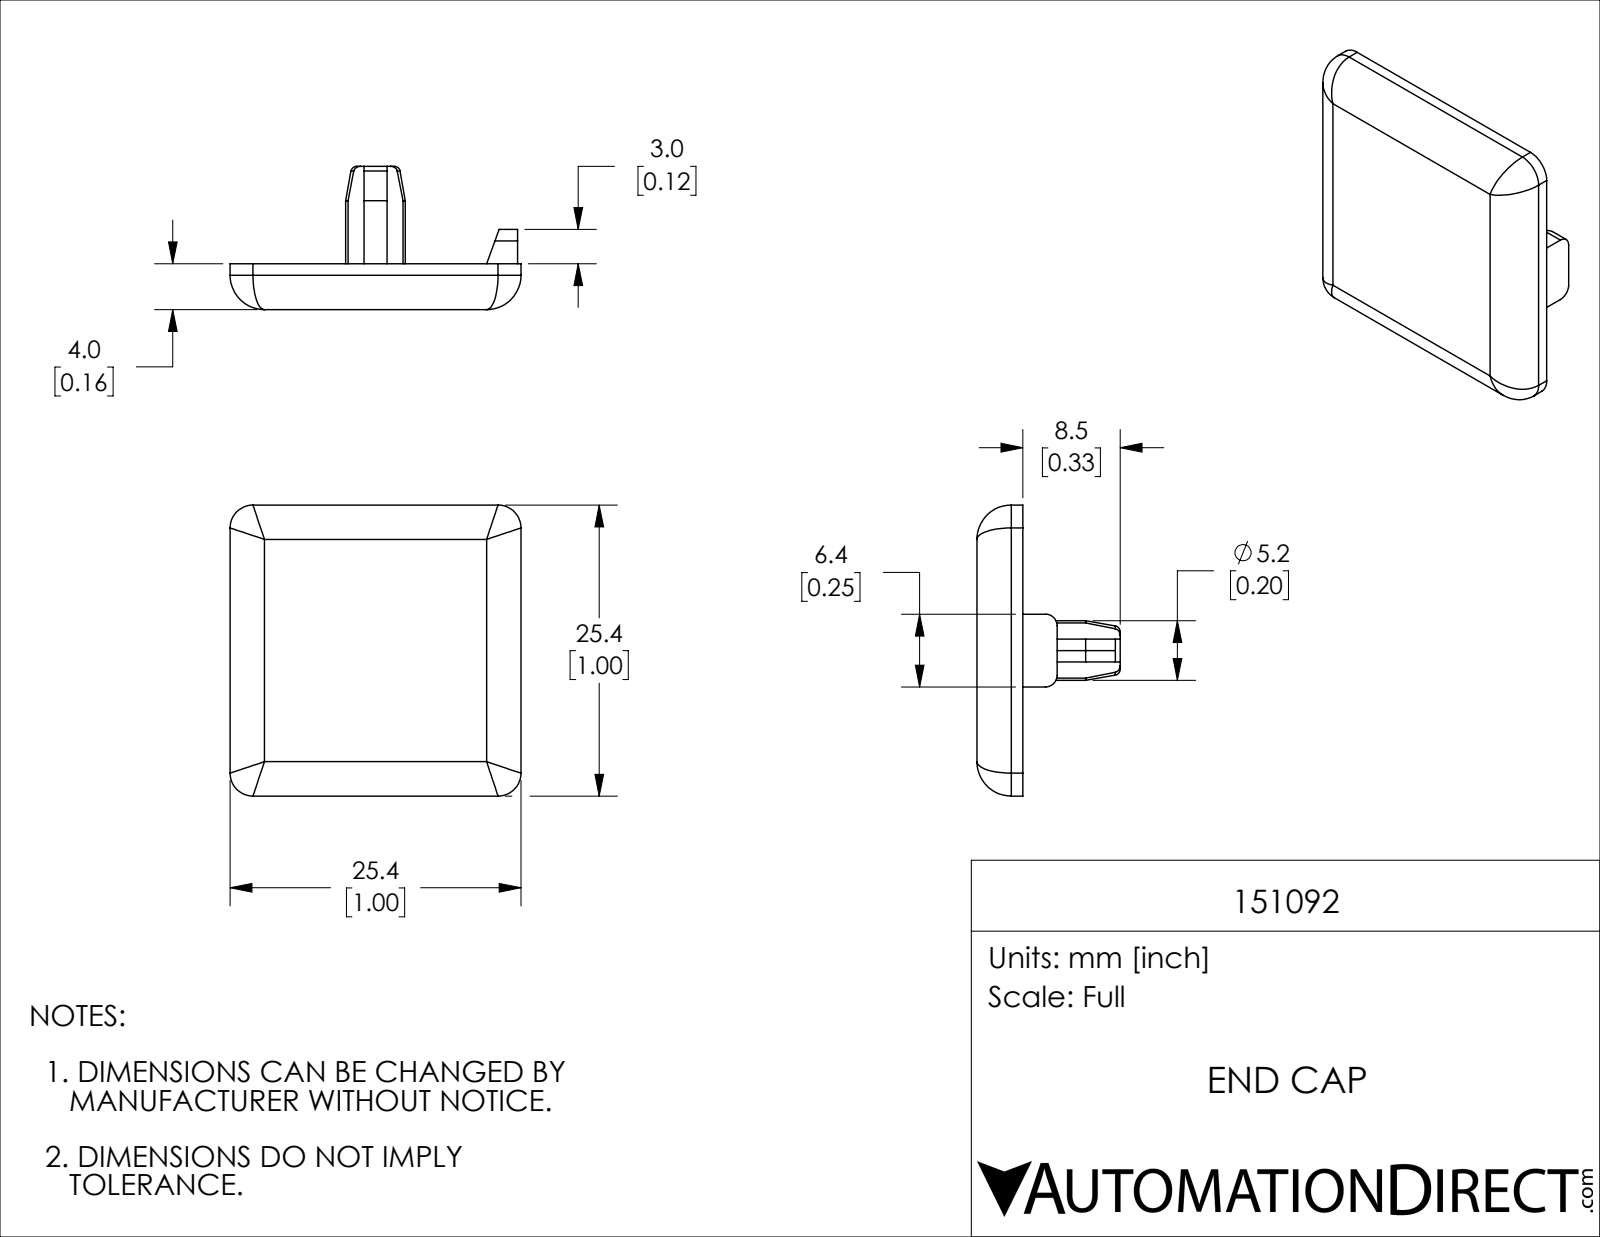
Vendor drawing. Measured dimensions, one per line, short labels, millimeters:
name: 151092
written by: SolidWorks 2021 (CONFIG_CONTROL_DESIGN)
unit: mm
bodies: 1 solid, 54 faces (25 planar, 15 cylindrical, 14 other)
size: 25.4 × 25.4 × 12.5
volume: 2 197 mm³; area: 1 838 mm²
rounds: 4× R2, 4× R3, 2× R1, 1× R2.6
face distances: 3, 4, 1, 11.7, 13.7, 22.4, 8.7, 10.7, 2, 25.4
